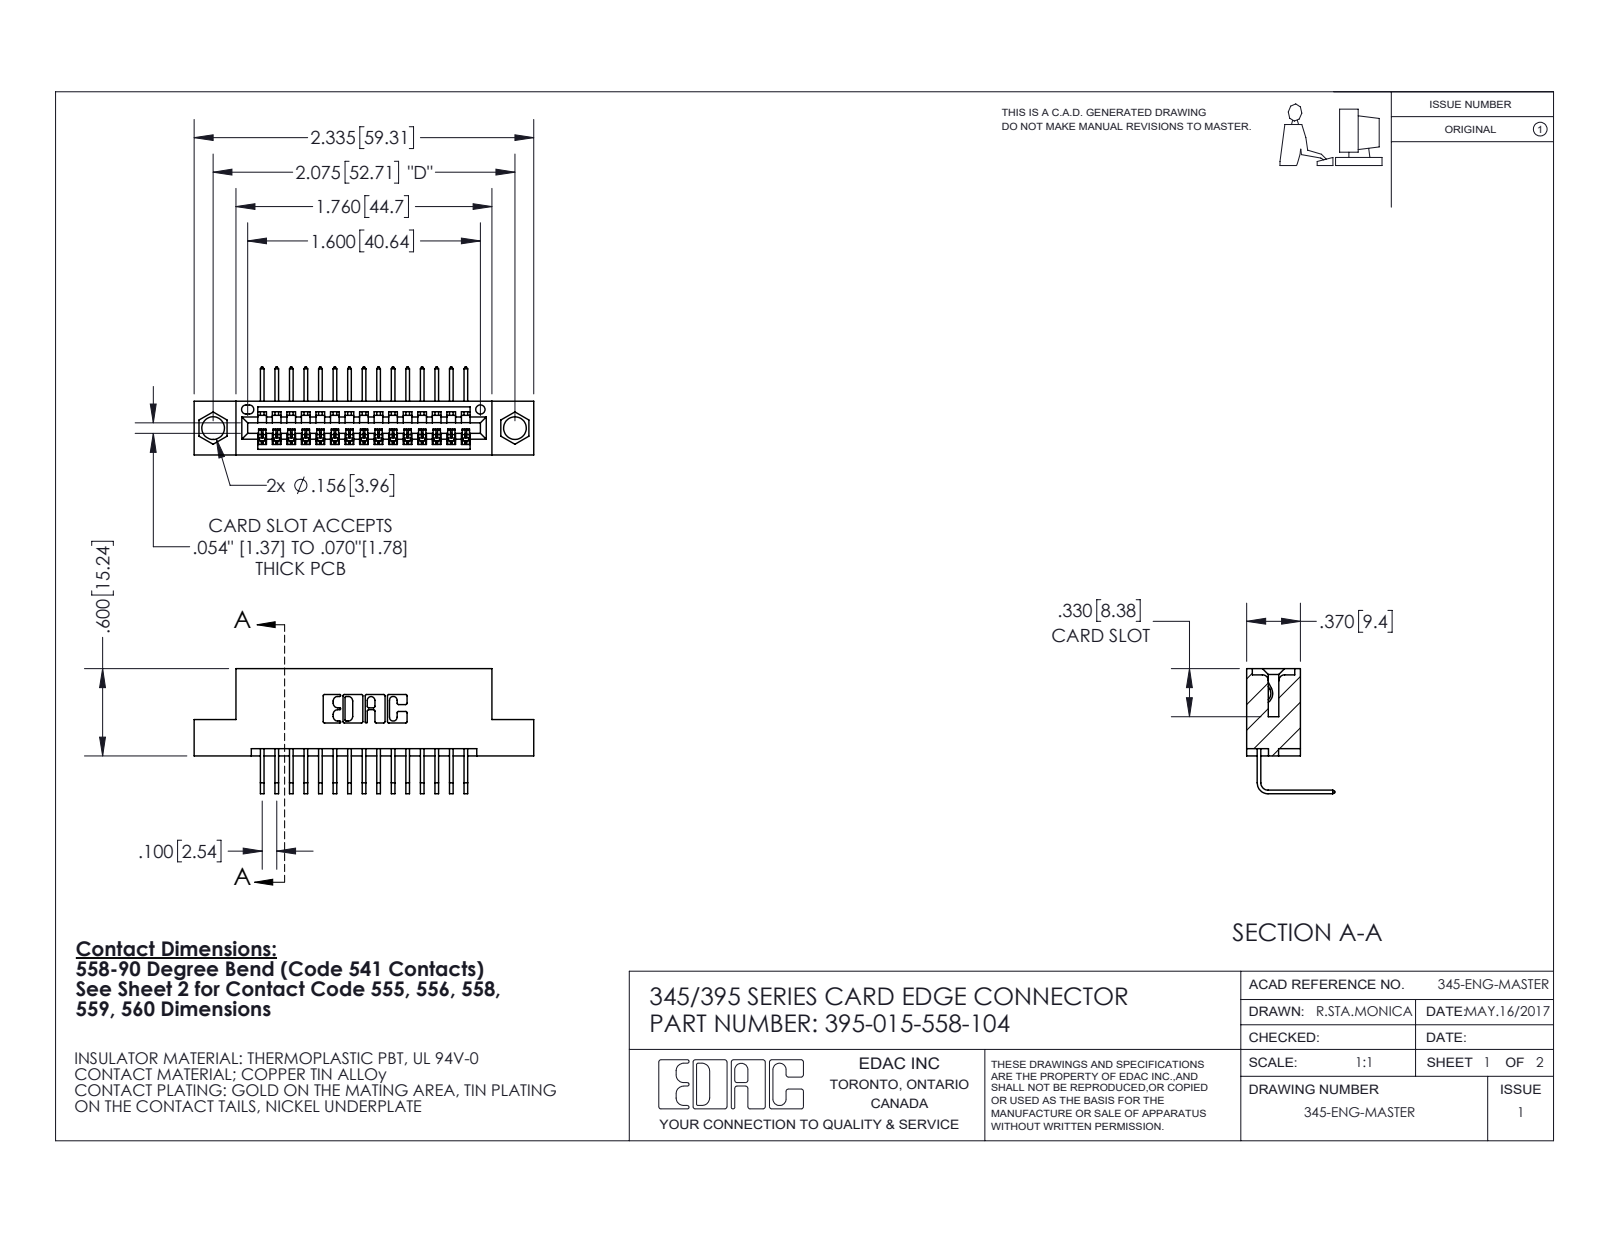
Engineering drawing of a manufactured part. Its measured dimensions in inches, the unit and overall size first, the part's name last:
Units: inches
Overall size (bounding box): 2.335 × 0.859 × 0.605
Round holes (diameter × count): ⌀0.156 ×2, ⌀0.064 ×1
Partial cylindrical surfaces — rounded edges, fillets, slot ends (radius × count): R0.006 ×30, R0.01 ×22, R0.007 ×6, R0.031 ×6, R0.026 ×3, R0.031 ×2, R0.04 ×2, R0.014 ×1
Main face-to-face distances: 0.072, 0.298, 0.2, 0.37, 0.098, 0.272, 0.025, 0.1, 0.225, 0.05
Hole centre spacings: 0.27, 1.842, 2.075
Volume: 0.327 in³ · Surface area: 10.67 in²
Bodies: 16 solids, 1040 faces (724 planar, 316 cylindrical, 0 other)
Part name (STEP PRODUCT): 395-015-558-104; 345 Part_Flush Mounting Lugs - 0.156 Dia-TI; 345-292-001_558 Tail - 2
STEP written by: SolidWorks 2020 (CONFIG_CONTROL_DESIGN)
